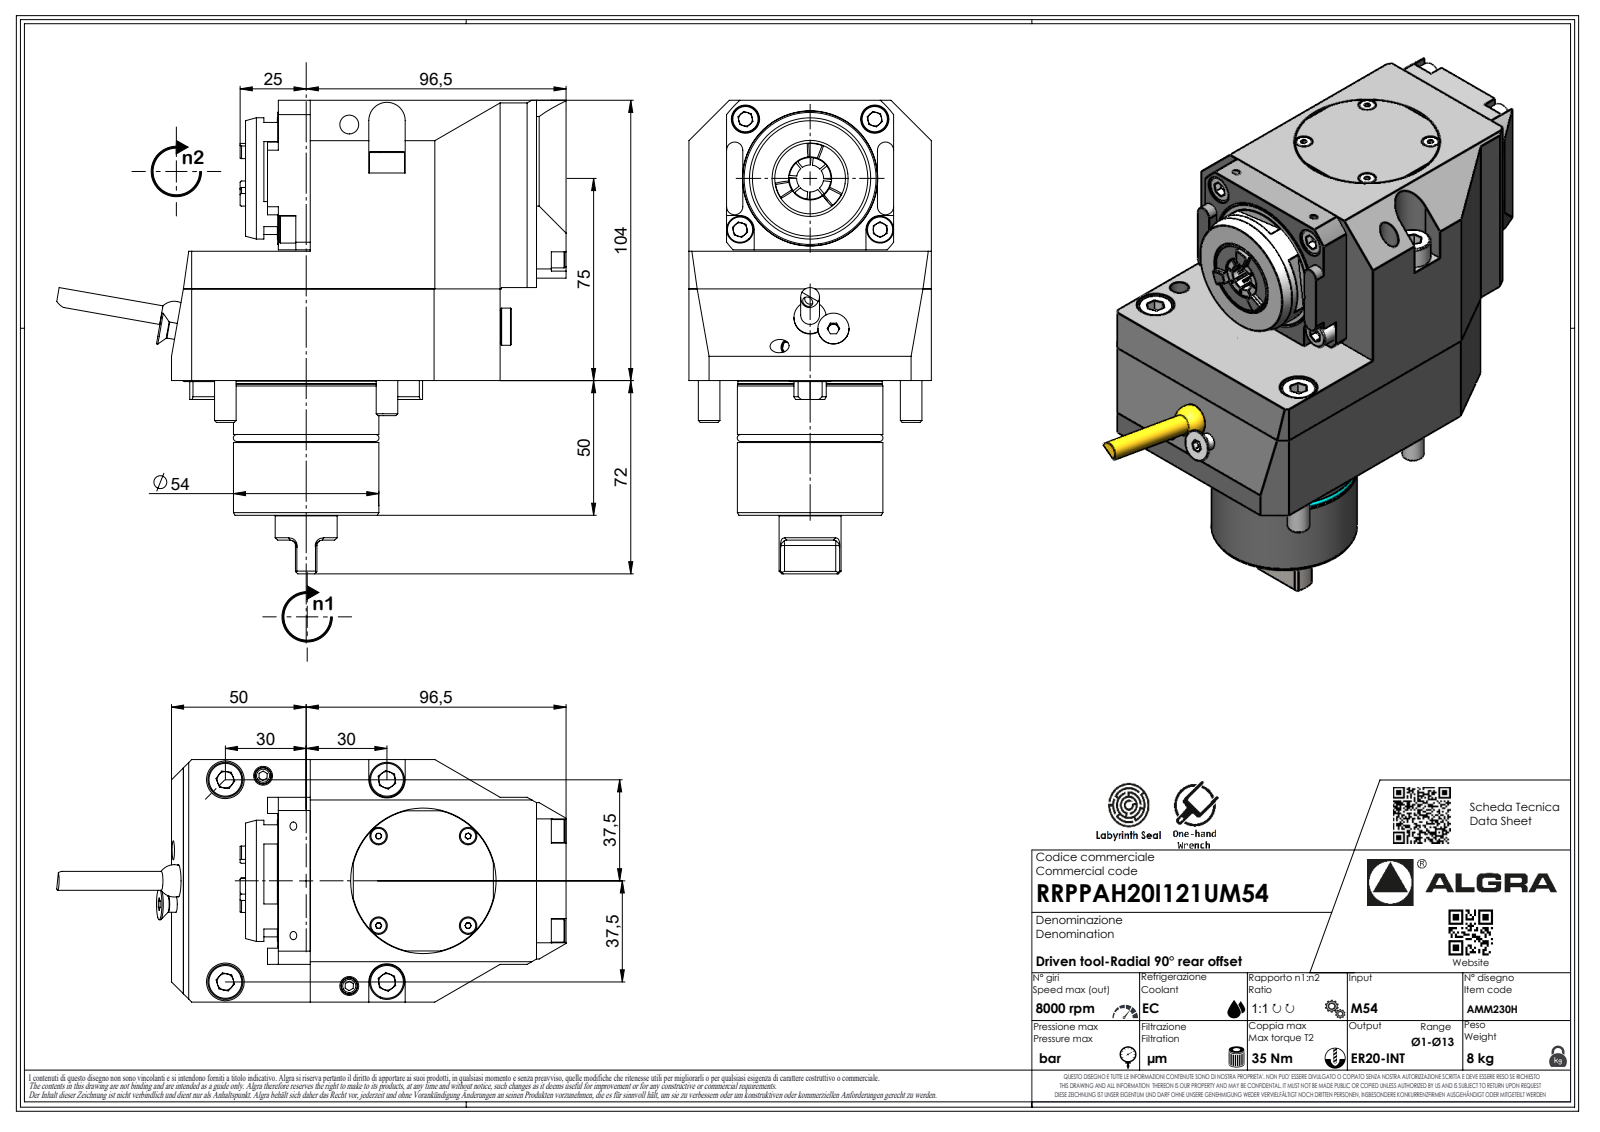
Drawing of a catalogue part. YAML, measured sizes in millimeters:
part_name: "RRPPAH20I121UM54"
step_written_by: "SolidWorks 2023 (AUTOMOTIVE_DESIGN)"
units: millimeters
bodies: {solids: 1, faces: 502, planar: 344, cylindrical: 67, other: 91}
overall_size: [194.12, 175.7, 90]
volume: 1100000
surface_area: 80846
round_holes:
  - {diameter: 2.1, count: 1}
  - {diameter: 4, count: 1}
round_bosses_or_shafts:
  - {diameter: 8, count: 4}
  - {diameter: 13, count: 2}
  - {diameter: 54, count: 1}
  - {diameter: 53.6, count: 1}
  - {diameter: 49.9, count: 1}
  - {diameter: 45, count: 1}
  - {diameter: 23, count: 1}
  - {diameter: 7, count: 1}
partial_cylinders:
  - {radius: 0.33, count: 7}
  - {radius: 0.52, count: 7}
  - {radius: 2, count: 7}
  - {radius: 3.7, count: 7}
  - {radius: 3, count: 4}
  - {radius: 6, count: 2}
  - {radius: 6.75, count: 2}
  - {radius: 0.21, count: 1}
face_to_face_distances: [104, 90, 48, 56, 14, 76, 24.5, 50, 98, 154]
